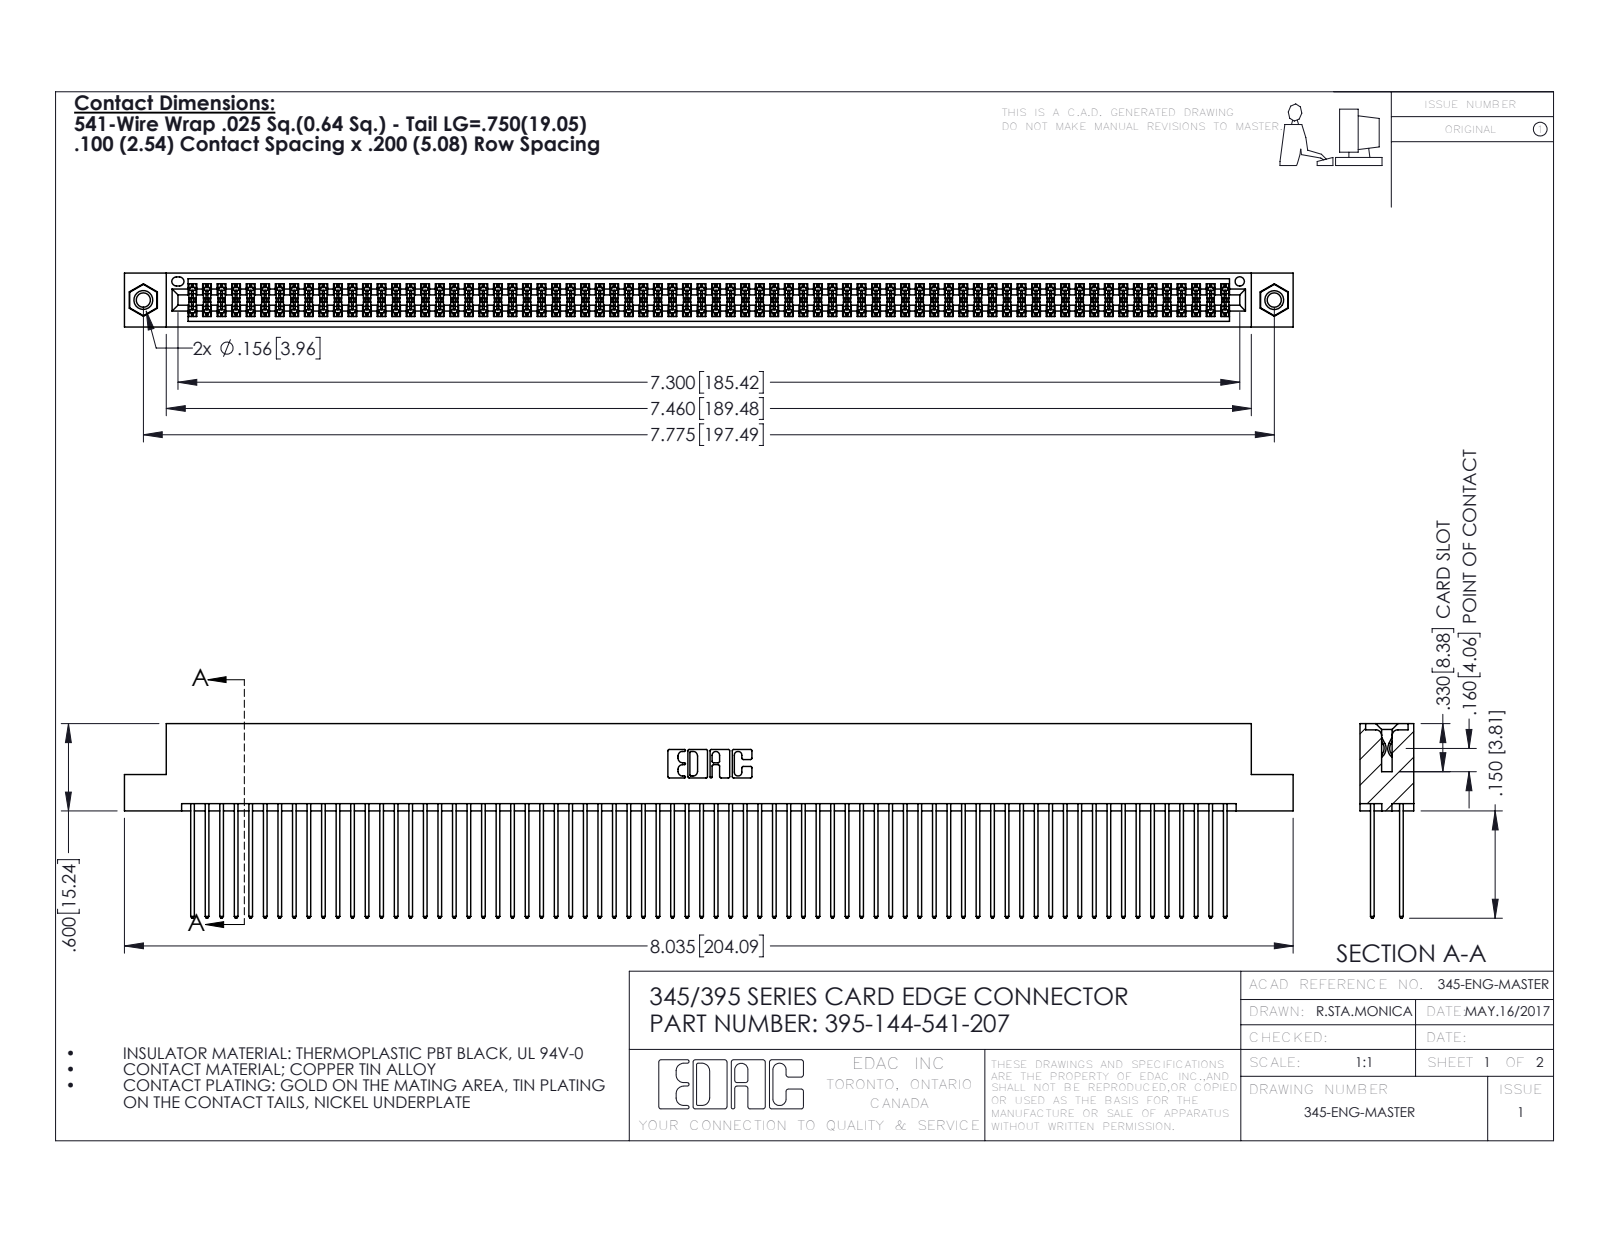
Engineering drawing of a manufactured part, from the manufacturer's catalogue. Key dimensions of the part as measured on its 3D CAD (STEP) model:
Part name (STEP PRODUCT): 345 Part_Flush Mounting Lugs - 0.156 Dia-TI; 345-250-001_345-250-005-103; 395-144-541-207; 345-292-001_345-293-141
STEP written by: SolidWorks 2016 (CONFIG_CONTROL_DESIGN)
Units: inches
Bodies: 147 solids, 7386 faces (4864 planar, 2506 cylindrical, 16 other)
Overall size (bounding box): 8.035 × 1.337 × 0.37
Volume: 1.276 in³ · Surface area: 54.89 in²
Round holes (diameter × count): ⌀0.098 ×2, ⌀0.125 ×2, ⌀0.156 ×2, ⌀0.064 ×1
Round bosses / shafts (diameter × count): ⌀0.155 ×2
Partial cylindrical surfaces — rounded edges, fillets, slot ends (radius × count): R0.006 ×216, R0.01 ×144, R0.01 ×22, R0.007 ×6, R0.031 ×6, R0.026 ×3, R0.014 ×2, R0.019 ×2
Main face-to-face distances: 0.072, 0.298, 0.2, 0.098, 0.272, 0.025, 0.225, 0.37, 0.175, 0.149
Hole centre spacings: 0.27, 7.539, 7.775
